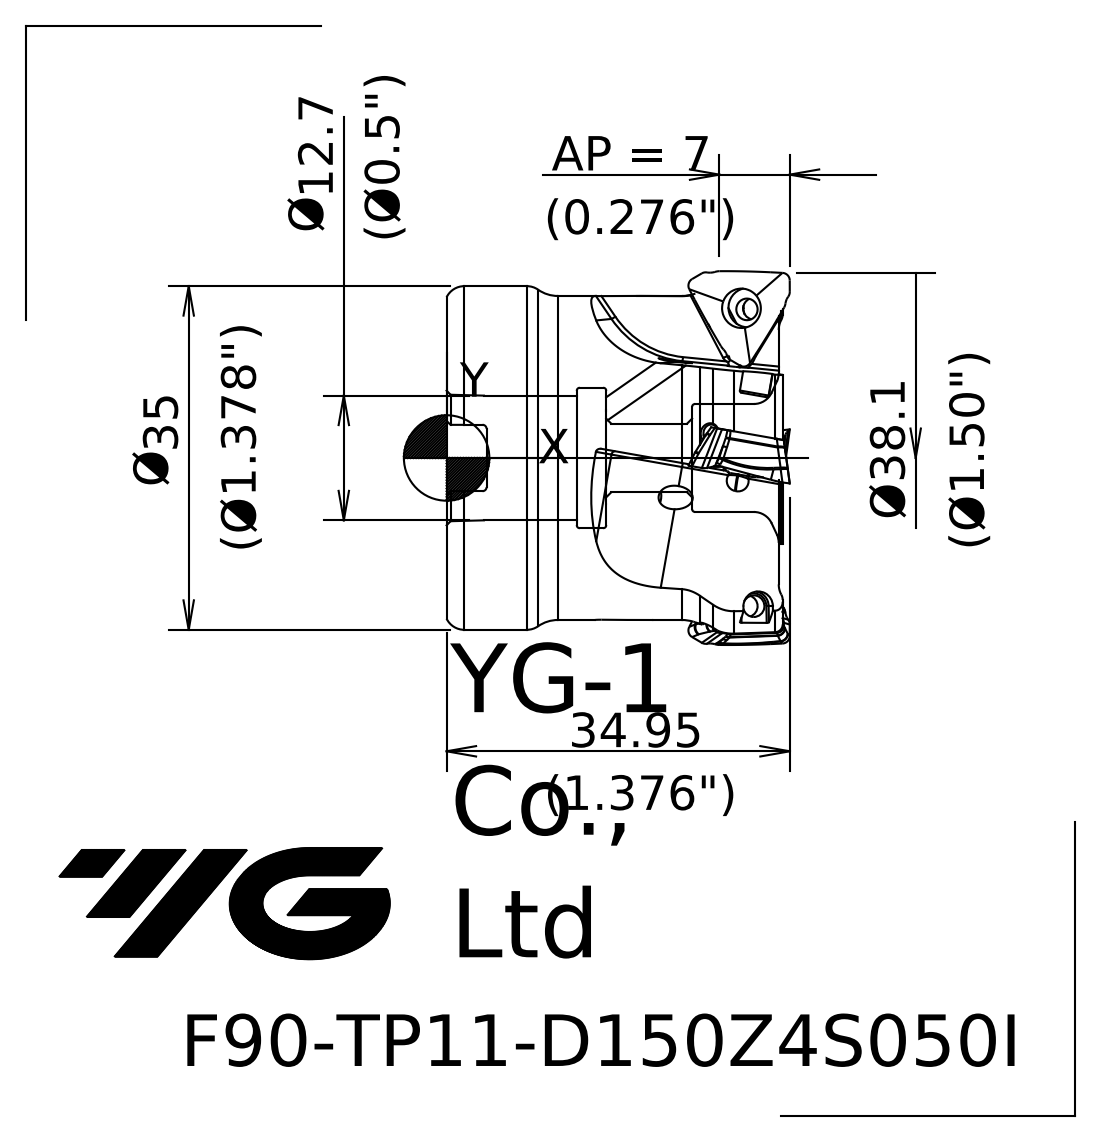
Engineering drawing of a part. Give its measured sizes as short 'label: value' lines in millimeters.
name: 10222DA0A397nvrx
written by: SIEMENS PLM Software NX 10.0 (AP203_CONFIGURATION_CONTROLLED_3D_DESIGN_OF_MECHANICAL_PARTS_AND_ASSEMBLIES_MIM_LF)
unit: mm
bodies: 1 solid, 95 faces (20 planar, 18 cylindrical, 57 other)
size: 38.19 × 38.19 × 34.95
volume: 26 750 mm³; area: 10 118 mm²
holes: 4× ⌀2, 4× ⌀2.4, 1× ⌀7.01, 1× ⌀11, 1× ⌀12.7, 1× ⌀14.3
bosses: 1× ⌀35, 1× ⌀33
rounds: 2× R0.4
face distances: 33.82, 29.76, 4.06, 17.57, 12.19, 16.25, 6.75, 8.83, 8.74, 20.93
